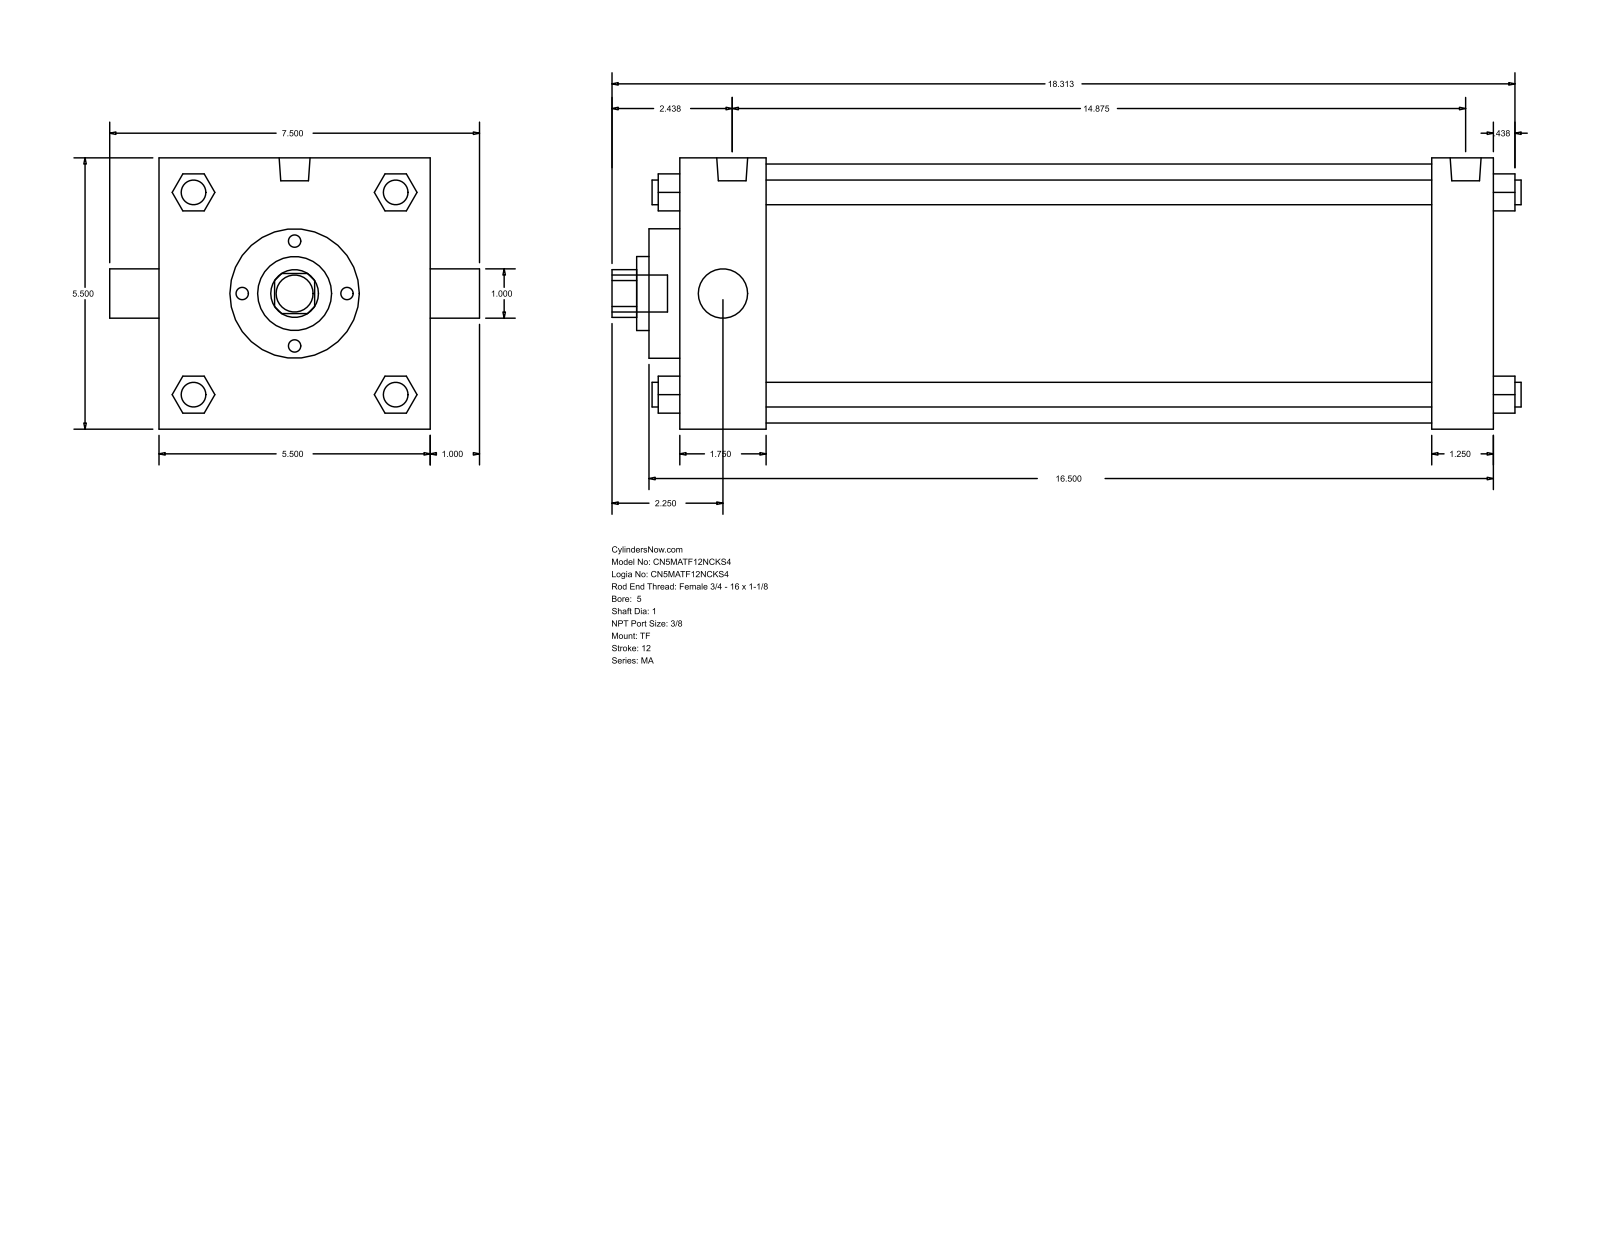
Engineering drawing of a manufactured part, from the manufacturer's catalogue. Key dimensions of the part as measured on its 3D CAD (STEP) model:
Part name (STEP PRODUCT): MA_TF__0500_1
STEP written by: GSSL Pune (CONFIG_CONTROL_DESIGN)
Units: millimetres
Bodies: 0 solids, 122 faces (93 planar, 29 cylindrical, 0 other)
Overall size (bounding box): 468.31 × 190.5 × 139.7
Round holes (diameter × count): ⌀25.4 ×2, ⌀38.1 ×1, ⌀66.67 ×1, ⌀133.35 ×1
Round bosses / shafts (diameter × count): ⌀12.7 ×4, ⌀11.11 ×3, ⌀15.93 ×2, ⌀19.05 ×1
Partial cylindrical surfaces — rounded edges, fillets, slot ends (radius × count): R12.29 ×1
Main face-to-face distances: 139.7, 419.1, 387.35, 31.75, 44.46, 342.89, 374.64, 15.87, 60.33, 403.22
